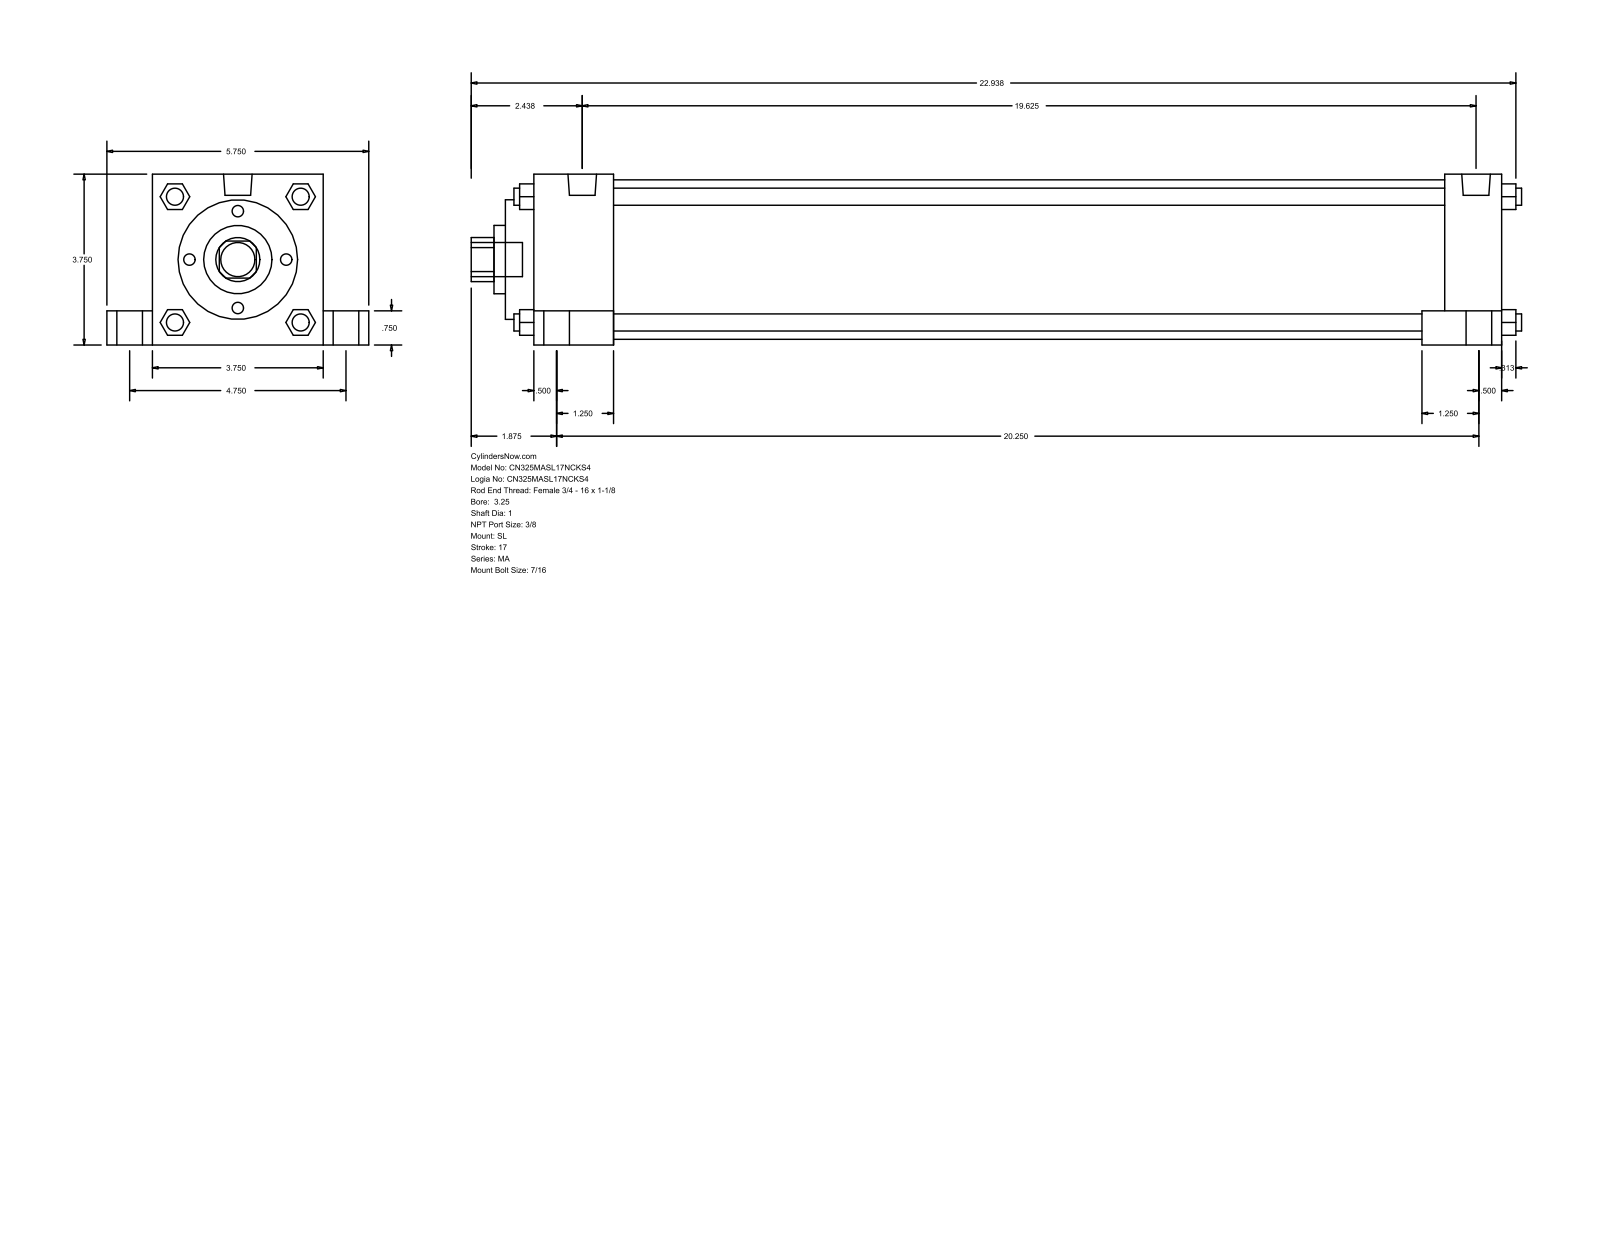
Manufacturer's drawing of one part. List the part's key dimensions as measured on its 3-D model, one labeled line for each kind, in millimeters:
Part name (STEP PRODUCT): MA_SL__0325_1
STEP written by: GSSL Pune (CONFIG_CONTROL_DESIGN)
Units: millimetres
Bodies: 0 solids, 150 faces (113 planar, 37 cylindrical, 0 other)
Overall size (bounding box): 585.79 × 146.05 × 95.25
Round holes (diameter × count): ⌀25.4 ×1, ⌀38.1 ×1, ⌀66.67 ×1, ⌀88.9 ×1
Round bosses / shafts (diameter × count): ⌀20.64 ×4, ⌀14.29 ×4, ⌀11.11 ×4, ⌀9.53 ×4, ⌀15.93 ×2, ⌀19.05 ×1
Partial cylindrical surfaces — rounded edges, fillets, slot ends (radius × count): R12.29 ×1
Main face-to-face distances: 95.24, 539.75, 15.87, 25.41, 120.65, 555.62, 19.05, 508, 31.75, 44.46
